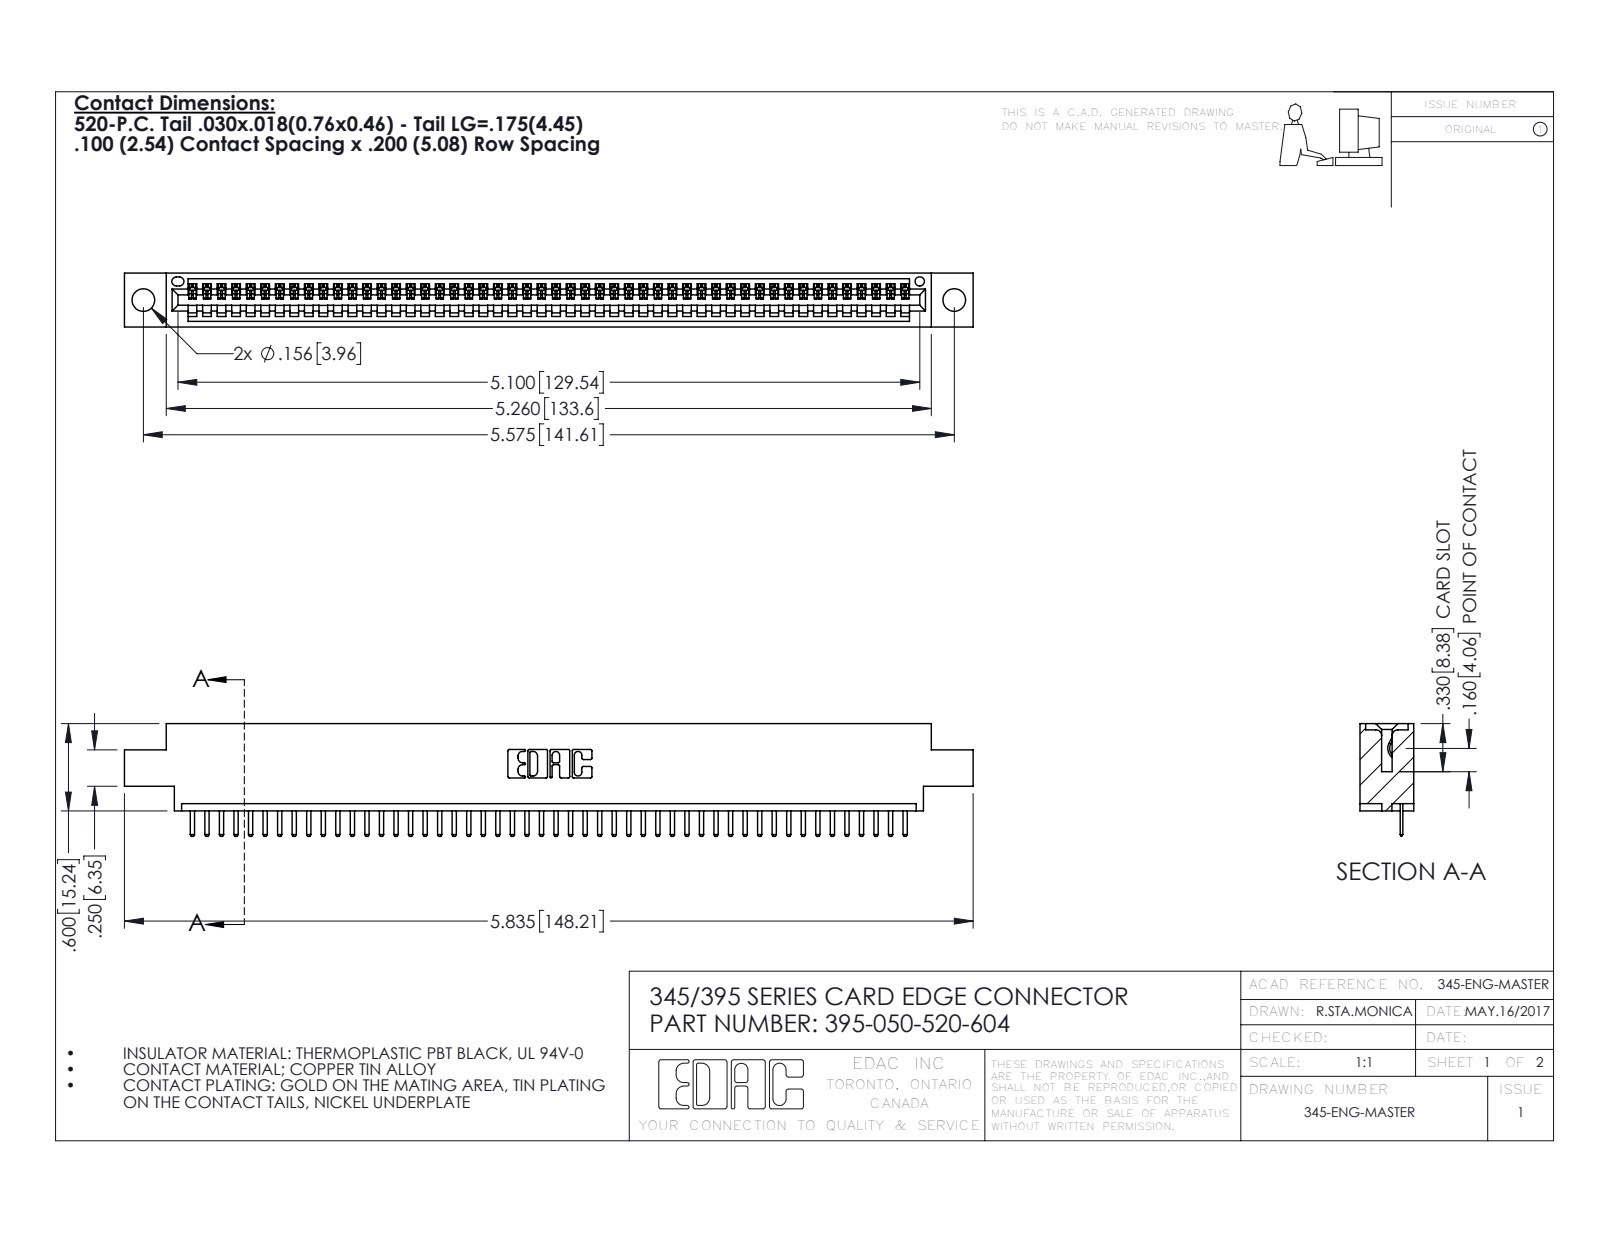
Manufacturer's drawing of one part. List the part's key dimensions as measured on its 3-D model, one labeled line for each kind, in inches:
Part name (STEP PRODUCT): 395-050-520-604; 345 Part_0.170 Offset - 0.156 Dia-TH; 345-292-001_345-293-120
STEP written by: SolidWorks 2016 (CONFIG_CONTROL_DESIGN)
Units: inches
Bodies: 51 solids, 3230 faces (2184 planar, 1046 cylindrical, 0 other)
Overall size (bounding box): 5.835 × 0.775 × 0.37
Volume: 0.842 in³ · Surface area: 27.76 in²
Round holes (diameter × count): ⌀0.156 ×2, ⌀0.064 ×1
Partial cylindrical surfaces — rounded edges, fillets, slot ends (radius × count): R0.01 ×102, R0.006 ×100, R0.01 ×22, R0.007 ×6, R0.031 ×6, R0.026 ×3, R0.031 ×2, R0.04 ×2
Main face-to-face distances: 0.298, 0.072, 0.37, 0.2, 0.098, 0.272, 0.025, 0.225, 0.072, 0.175
Hole centre spacings: 0.27, 5.339, 5.575
